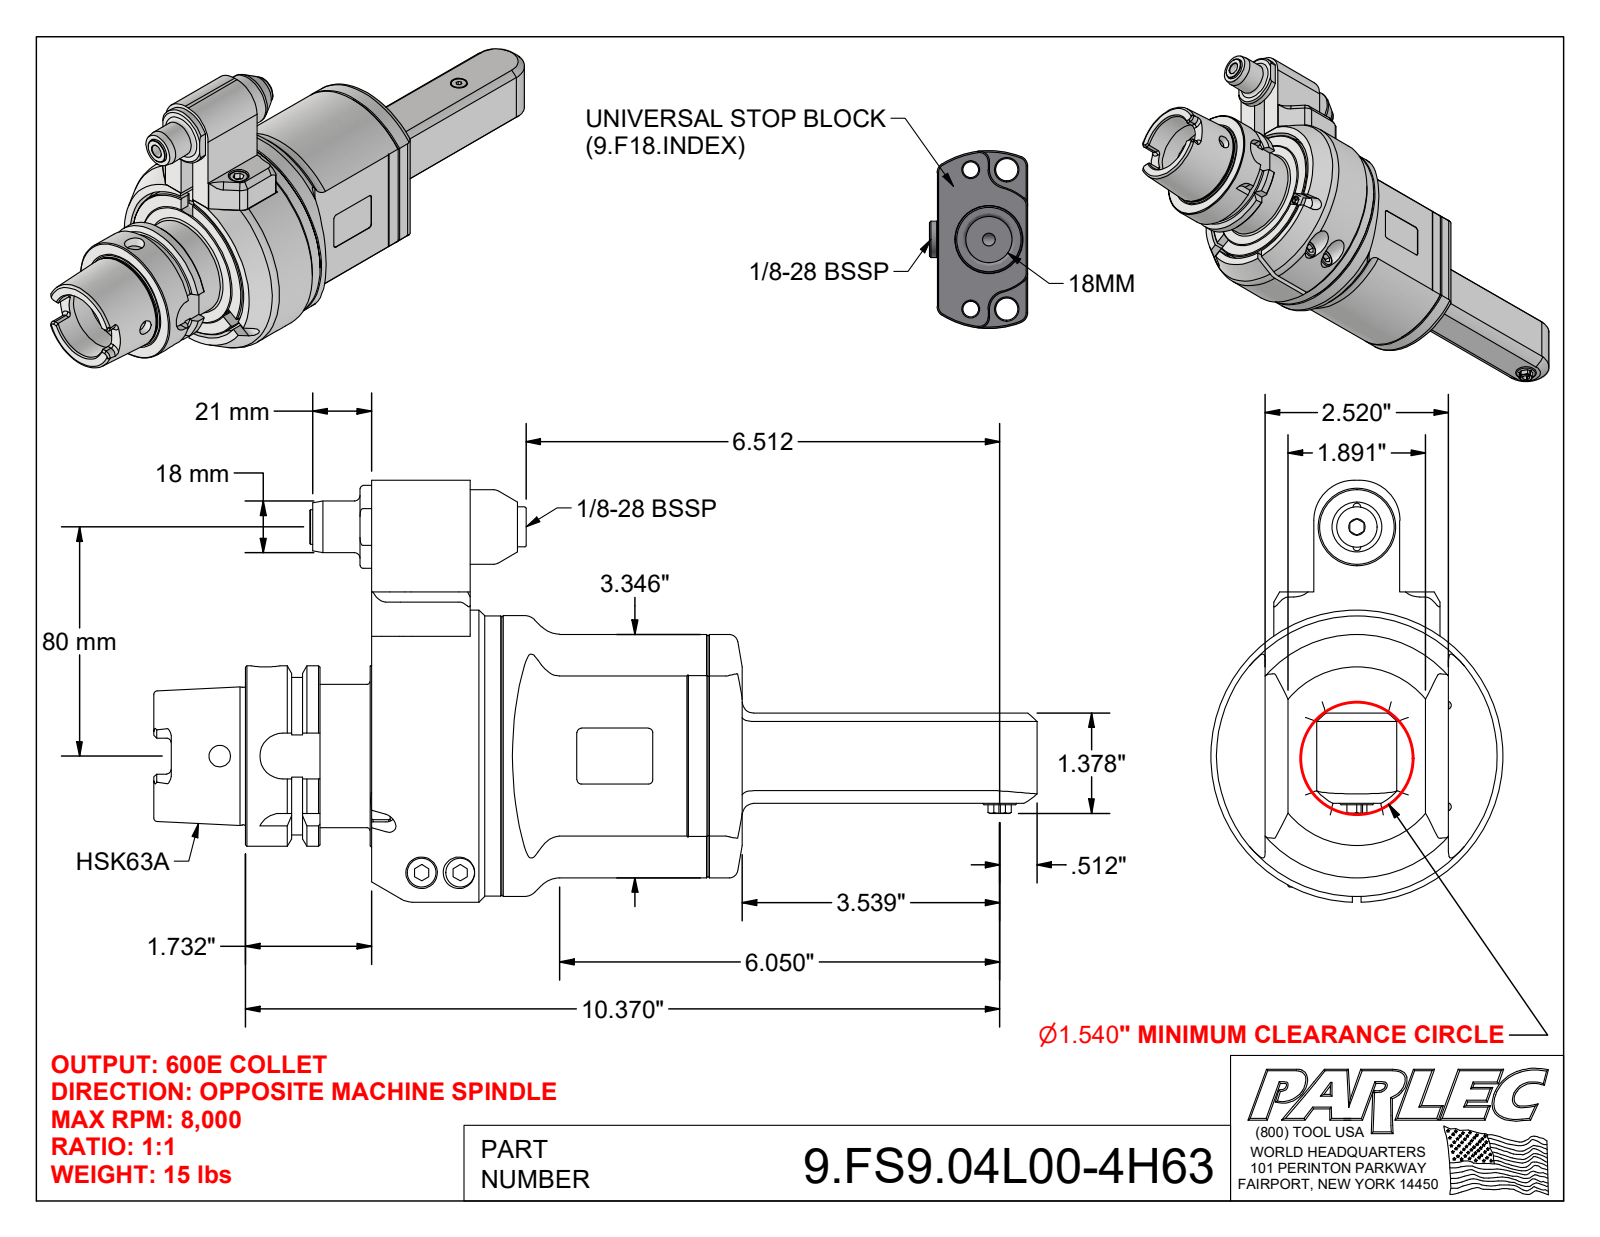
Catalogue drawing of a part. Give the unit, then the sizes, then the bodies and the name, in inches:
Units: inches
Overall size (bounding box): 12.142 × 5.796 × 4.016
Round holes (diameter × count): ⌀0.102 ×2, ⌀0.118 ×2, ⌀0.165 ×2, ⌀0.197 ×2, ⌀0.335 ×2, ⌀0.409 ×2, ⌀0.433 ×2, ⌀0.492 ×2, ⌀0.098 ×1, ⌀0.157 ×1, ⌀0.256 ×1, ⌀0.276 ×1
Round bosses / shafts (diameter × count): ⌀0.394 ×4, ⌀0.236 ×4, ⌀0.315 ×3, ⌀0.709 ×2, ⌀0.098 ×2, ⌀4.016 ×1, ⌀3.858 ×1, ⌀3.85 ×1
Partial cylindrical surfaces — rounded edges, fillets, slot ends (radius × count): R0.059 ×10, R0.157 ×10, R0.079 ×8, R0.113 ×4, R0.315 ×4, R0.551 ×3, R0.02 ×2, R0.039 ×2
Main face-to-face distances: 0.709, 1.102, 0.098, 1.378, 0.276, 1.811, 1.555, 1.28, 0.177, 0.197
Hole centre spacings: 0.276, 0.512, 0.551, 1.081, 1.72, 2.226, 2.67, 2.764
Volume: 62.88 in³ · Surface area: 237.4 in²
Bodies: 5 solids, 539 faces (267 planar, 139 cylindrical, 133 other)
Part name (STEP PRODUCT): 9.FS9.04L00-4H63; 9_GA1_568_2 (EVO, Type 1, HSK63A, 80mm); 9FL1ATC; 9HSK631ATC (+4 more)
STEP written by: Autodesk Inventor 2022 (AUTOMOTIVE_DESIGN)
